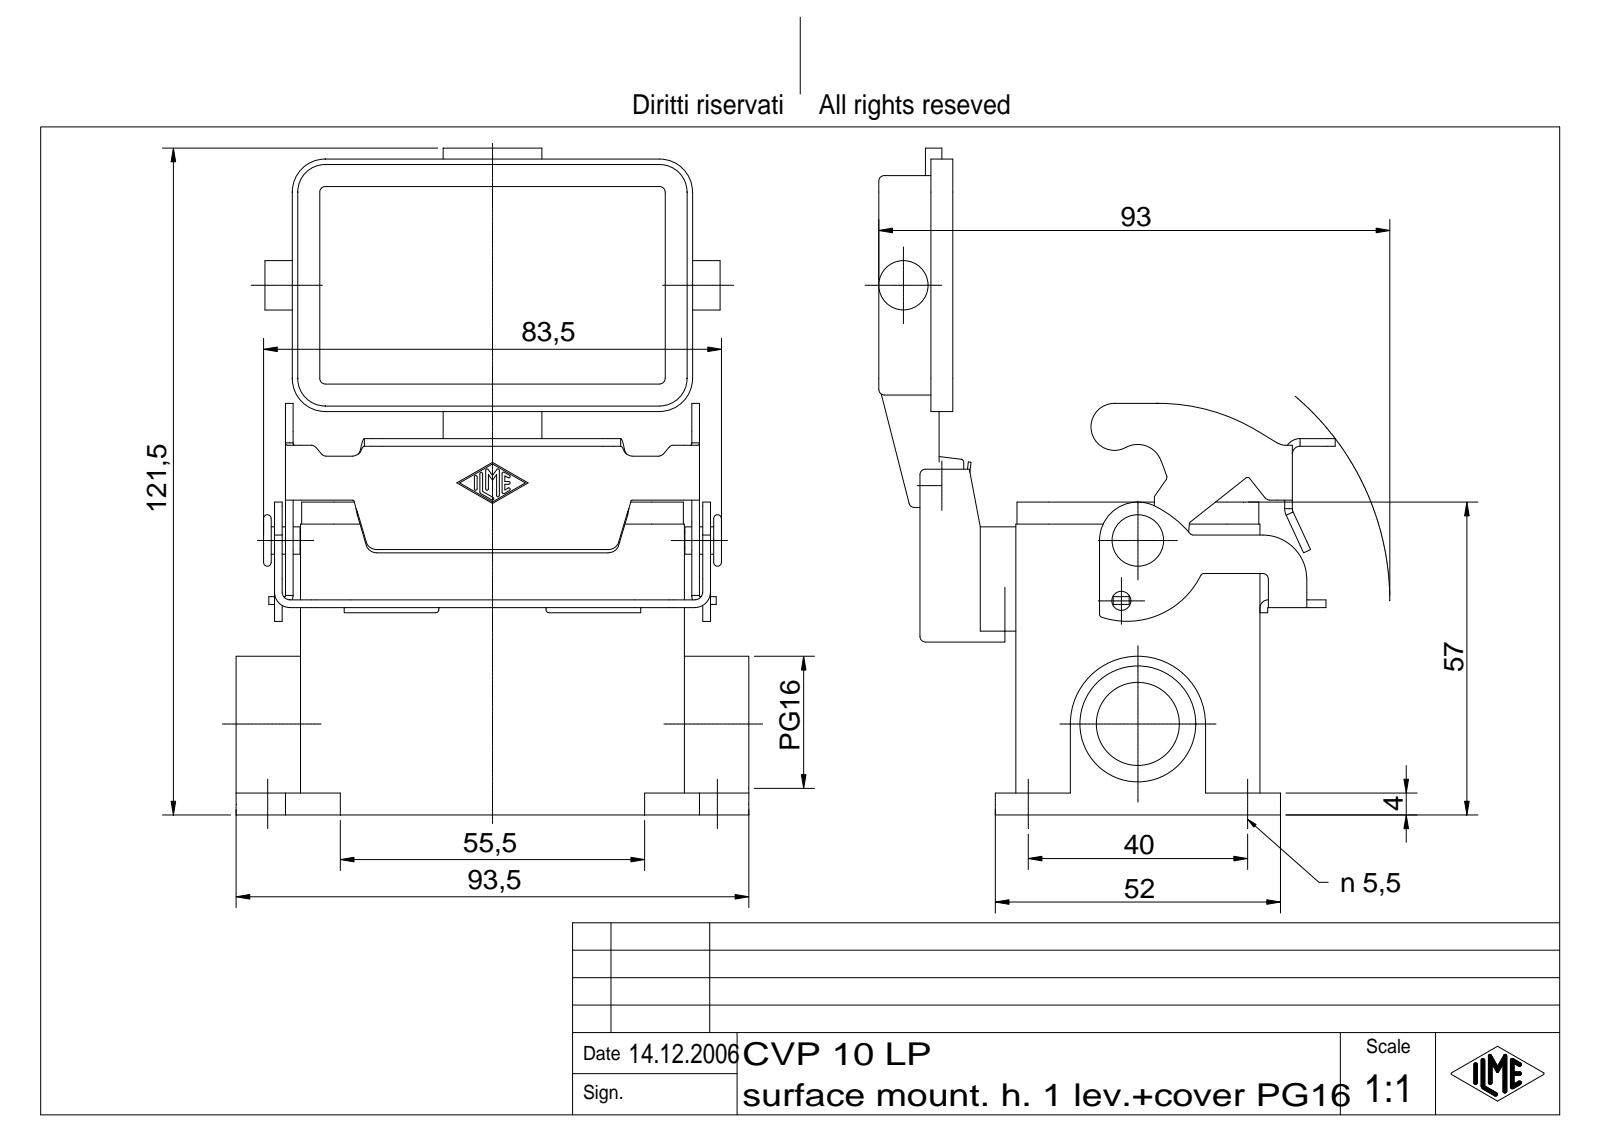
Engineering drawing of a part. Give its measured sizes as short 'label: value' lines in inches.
name: CVP 10 LP
written by: Autodesk Inventor 7 (AUTOMOTIVE_DESIGN)
unit: in
bodies: 4 solids, 590 faces (232 planar, 193 cylindrical, 165 other)
size: 4.783 × 3.681 × 3.277
volume: 6.258 in³; area: 98.61 in²
holes: 4× ⌀0.217, 1× ⌀0.138, 1× ⌀0.157, 1× ⌀0.597, 1× ⌀0.833
bosses: 2× ⌀0.197, 1× ⌀0.354, 1× ⌀0.276, 1× ⌀0.126, 1× ⌀0.118
rounds: 32× R0.039, 15× R0.01, 10× R0.02, 9× R0.059, 8× R0.236, 7× R0.079, 6× R0.055, 6× R0.11
face distances: 0.157, 1.594, 0.079, 0.394, 1.752, 2.736, 0.059, 2.579, 0.984, 1.437
hole spacings: 1.575, 3.228, 3.592, 0.891
